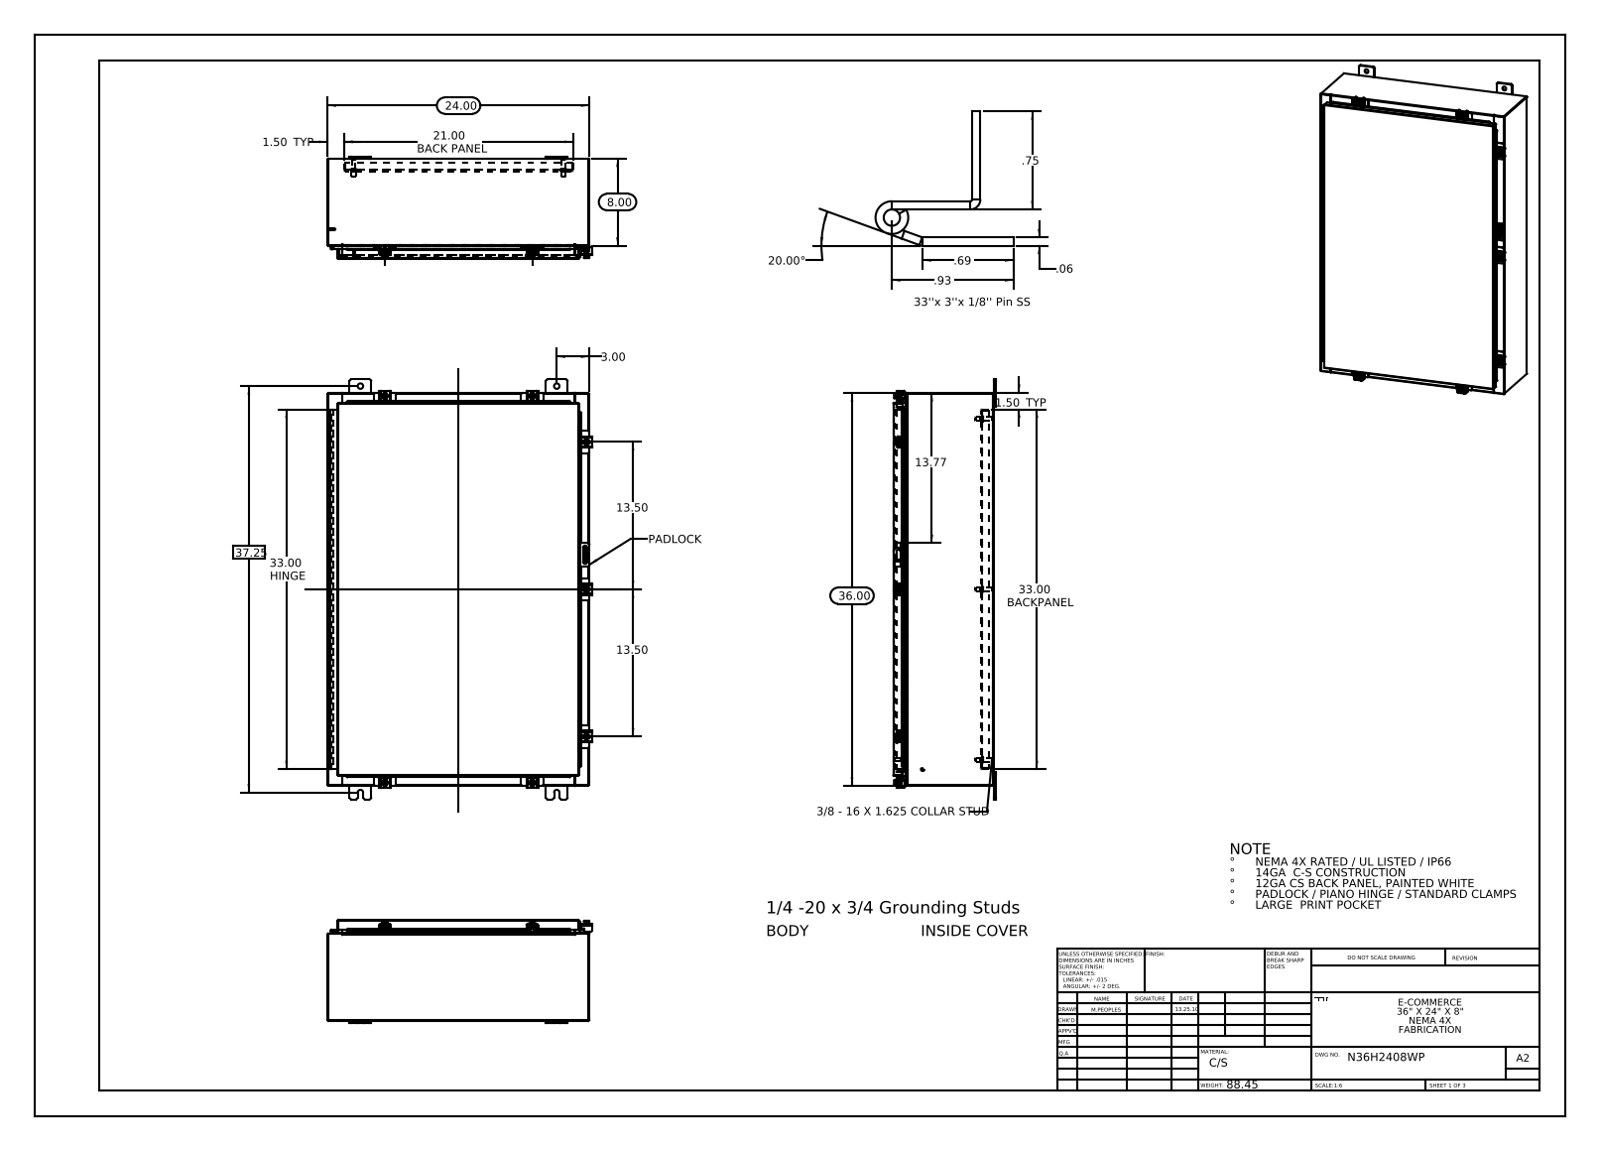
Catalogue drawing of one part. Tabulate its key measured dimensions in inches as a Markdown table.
| quantity | value |
| --- | --- |
| part name | N36H2408SSWP Top; N36H2408SSWP 125 Pin Hinge; N36H2408SSWP Body; N36H2408SSWP Hinge Cover Side (+8 more) |
| STEP written by | SolidWorks 2013 (CONFIG_CONTROL_DESIGN) |
| units | inches |
| bodies | 56 solids, 2210 faces (1144 planar, 930 cylindrical, 136 other) |
| overall size | 38.5 × 24.211 × 9.389 |
| volume | 310.7 in³ |
| surface area | 7 748 in² |
| round holes (diameter × count) | 0.5 × 10, 0.213 × 7, 0.26 × 7, 0.125 × 2 |
| round bosses / shafts (diameter × count) | 0.25 × 8, 0.5 × 7, 0.399 × 7, 0.625 × 6, 0.375 × 6, 0.33 × 6, 0.315 × 2, 0.236 × 2 |
| partial cylindrical surfaces (radius × count) | 0.06 × 34, 0.013 × 27, 0.19 × 24, 0.088 × 21, 0.12 × 14, 0.141 × 14, 0.05 × 11, 0.08 × 10 |
| main face-to-face distances | 0.075, 9.126, 9.051, 9.201, 0.104, 1, 1.075, 8.051, 8.126, 1.179 |
| hole center spacings | 13.5, 15.625, 17.957, 24.793, 33.474, 37.154, 19.25, 1.858 |
